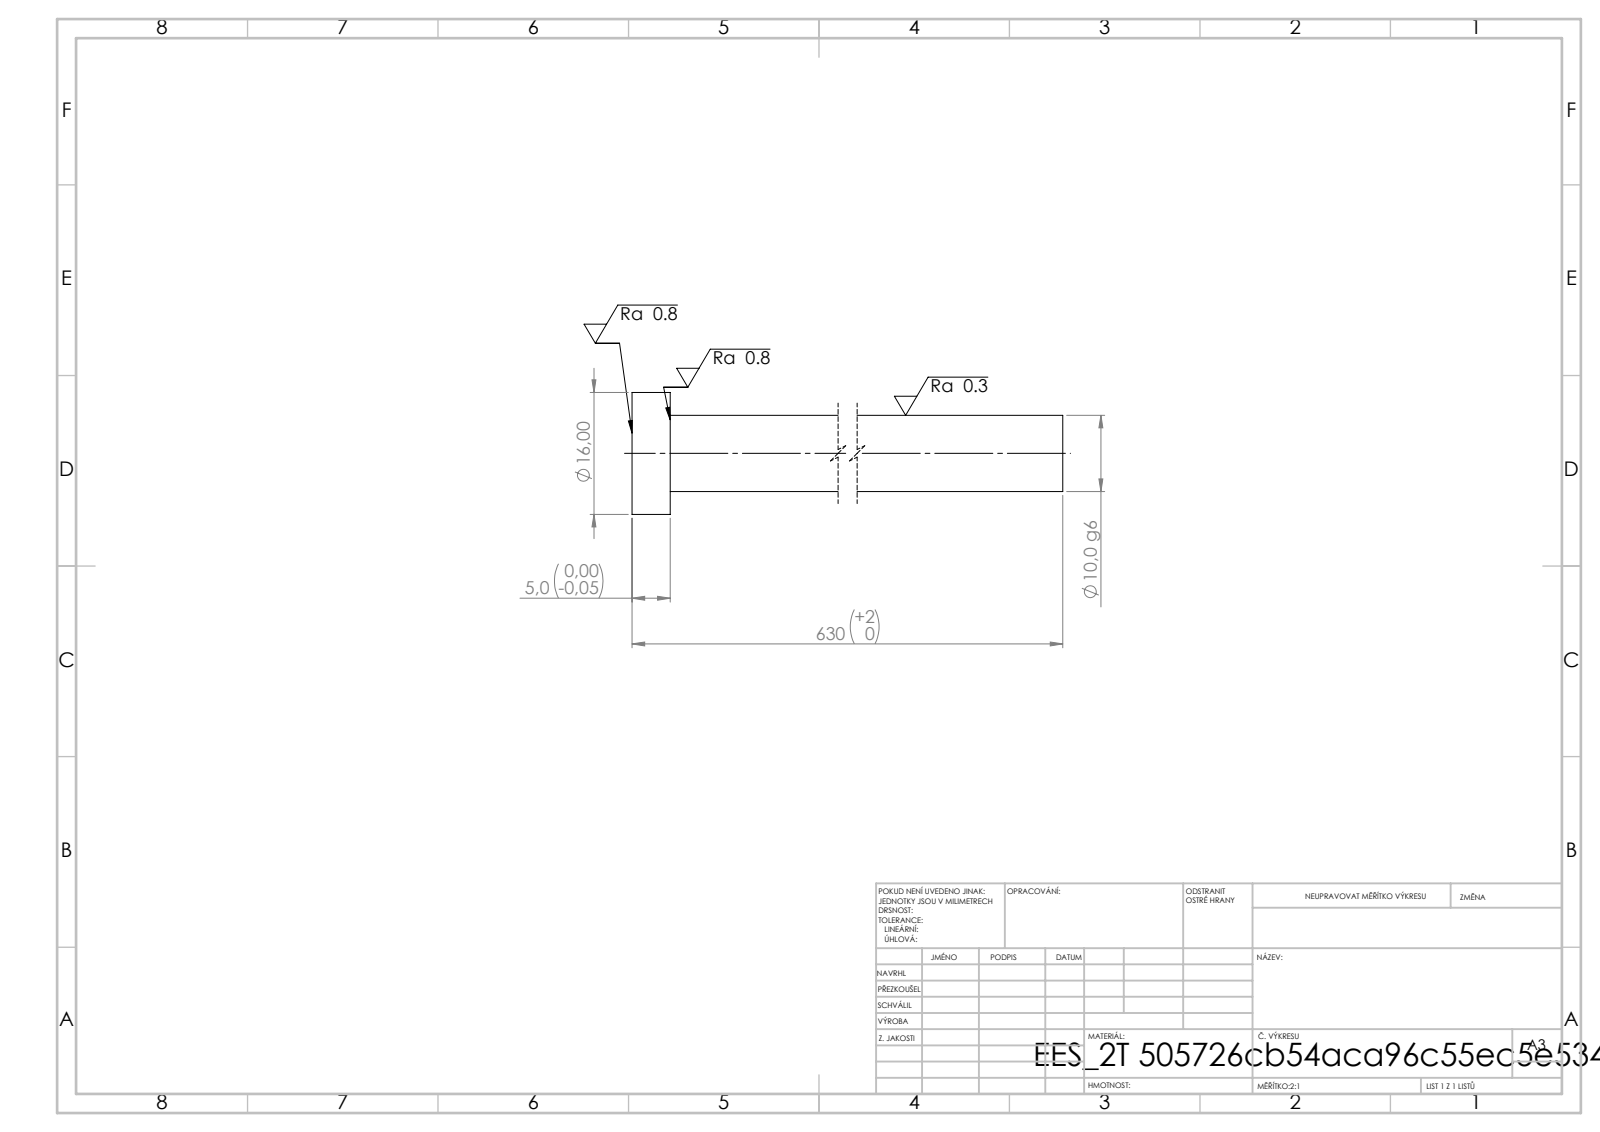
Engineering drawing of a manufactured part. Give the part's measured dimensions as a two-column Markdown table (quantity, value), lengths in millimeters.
| quantity | value |
| --- | --- |
| STEP written by | SolidWorks 2019 (CONFIG_CONTROL_DESIGN) |
| units | millimeters |
| bodies | 1 solid, 7 faces (3 planar, 4 cylindrical, 0 other) |
| overall size | 630 × 16 × 16 |
| volume | 50 093 mm³ |
| surface area | 20 288 mm² |
| round bosses / shafts (diameter × count) | 16 × 1, 10 × 1 |
| main face-to-face distances | 5, 630, 625 |
